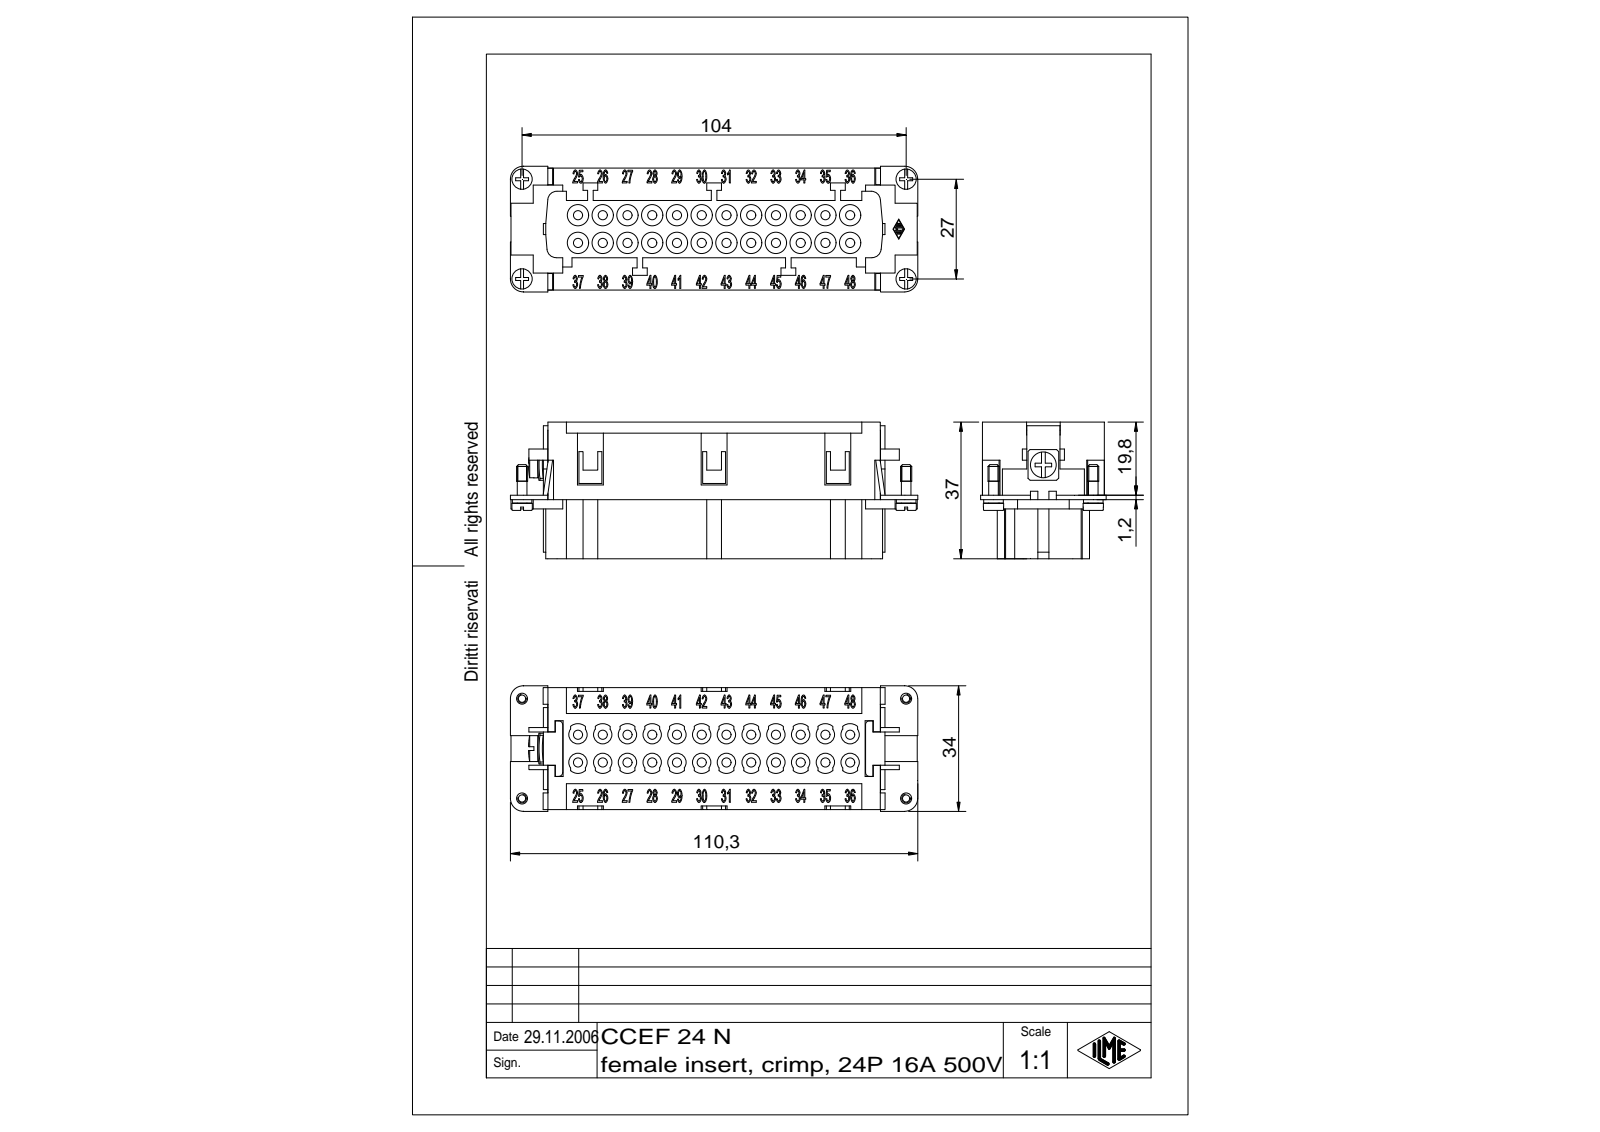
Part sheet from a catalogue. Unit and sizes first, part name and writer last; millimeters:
Units: millimetres
Overall size (bounding box): 110.3 × 37 × 34
Round holes (diameter × count): ⌀3.24 ×1
Round bosses / shafts (diameter × count): ⌀5.5 ×2, ⌀5.3 ×2, ⌀3 ×2, ⌀2.6 ×2, ⌀7 ×1
Partial cylindrical surfaces — rounded edges, fillets, slot ends (radius × count): R2.5 ×16, R0.1 ×14, R3 ×12, R1 ×2, R3.5 ×2, R5.5 ×1
Main face-to-face distances: 24.25, 8.75, 3, 33, 21, 15.5, 18, 16, 37, 34
Volume: 69 847 mm³ · Surface area: 33 797 mm²
Bodies: 1 solid, 2304 faces (1009 planar, 86 cylindrical, 1209 other)
Part name (STEP PRODUCT): CCEF 24 N
STEP written by: Autodesk Inventor 7 (AUTOMOTIVE_DESIGN)
